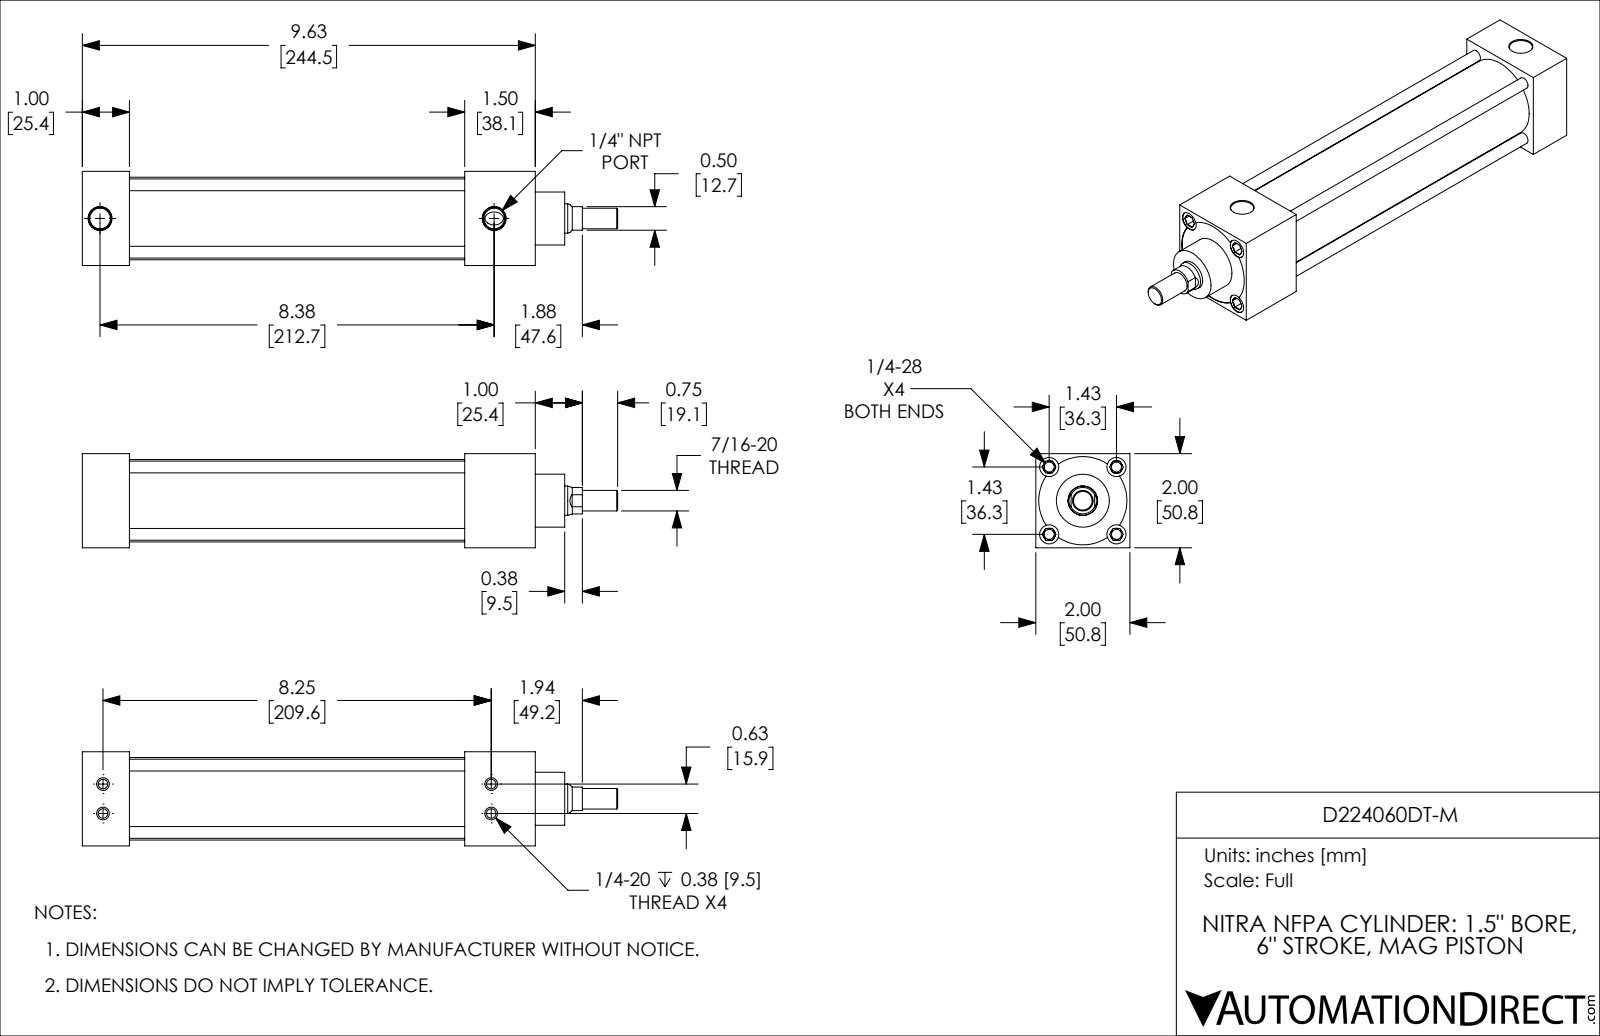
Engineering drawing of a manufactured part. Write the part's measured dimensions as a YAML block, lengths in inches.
part_name: "D224060DT-M; D224060DT-M_PISTON_KK1; D224060DT-M_BODY"
step_written_by: "SolidWorks 2019 (CONFIG_CONTROL_DESIGN)"
units: inches
bodies: {solids: 2, faces: 203, planar: 58, cylindrical: 65, other: 80}
overall_size: [11.375, 2, 2]
volume: 20.02
surface_area: 169.2
round_holes:
  - {diameter: 0.201, count: 4}
  - {diameter: 0.213, count: 4}
  - {diameter: 0.406, count: 4}
  - {diameter: 0.438, count: 2}
  - {diameter: 0.626, count: 1}
  - {diameter: 1.501, count: 1}
round_bosses_or_shafts:
  - {diameter: 0.25, count: 4}
  - {diameter: 1.751, count: 1}
  - {diameter: 1.499, count: 1}
  - {diameter: 1.125, count: 1}
  - {diameter: 0.624, count: 1}
  - {diameter: 0.437, count: 1}
partial_cylinders:
  - {radius: 0.281, count: 1}
  - {radius: 0.937, count: 1}
face_to_face_distances: [2, 1, 8.125, 7.125, 2.125, 9.62, 8.62, 1.495, 1.125, 6]
hole_center_spacings: [0.319, 1.011, 1.43, 0.625, 2.022, 8.25, 8.274, 8.318]
